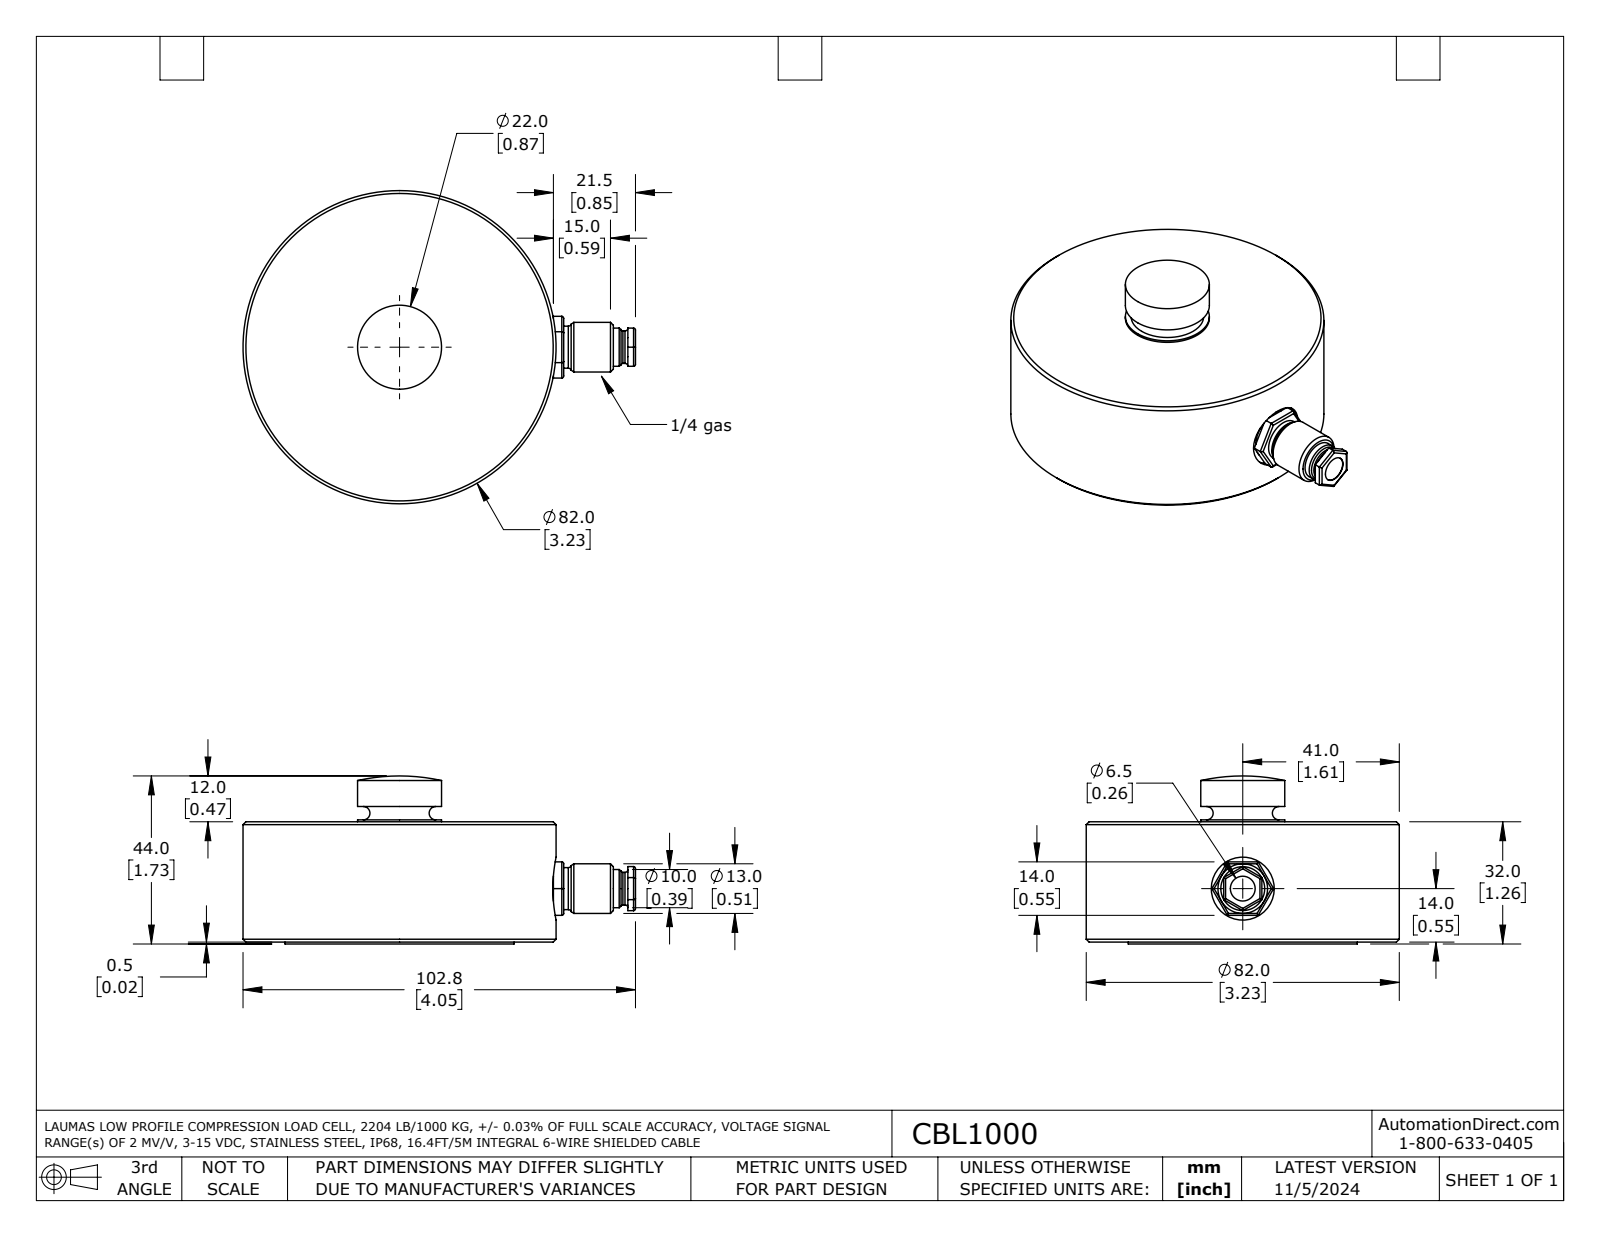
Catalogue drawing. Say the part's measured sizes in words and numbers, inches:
The part is named "CBL1000". Its 3-D file was written by "SolidWorks 2021 (AUTOMOTIVE_DESIGN)". It is 2 solids with 86 faces: 31 planar, 36 cylindrical and 19 other. Overall it measures 4.047 by 3.228 by 1.732 inches. Its volume is 10.42 cubic inches and its surface area 32.65 square inches. Round holes: 1 of diameter 0.256, 1 of diameter 0.65, 1 of diameter 2.15. Round bosses or shafts: 1 of diameter 3.228, 1 of diameter 2.362, 1 of diameter 0.866, 1 of diameter 0.531, 1 of diameter 0.512, 1 of diameter 0.433, 1 of diameter 0.394, 1 of diameter 0.335. Partial cylindrical surfaces (rounded edges, fillets, slot ends): 12 of radius 0.02. The main face-to-face distances are 1.211, 0.03, 1.24, 0.02, 1.26, 0.049, 0.138, 1.28, 1.23, 1.417.
